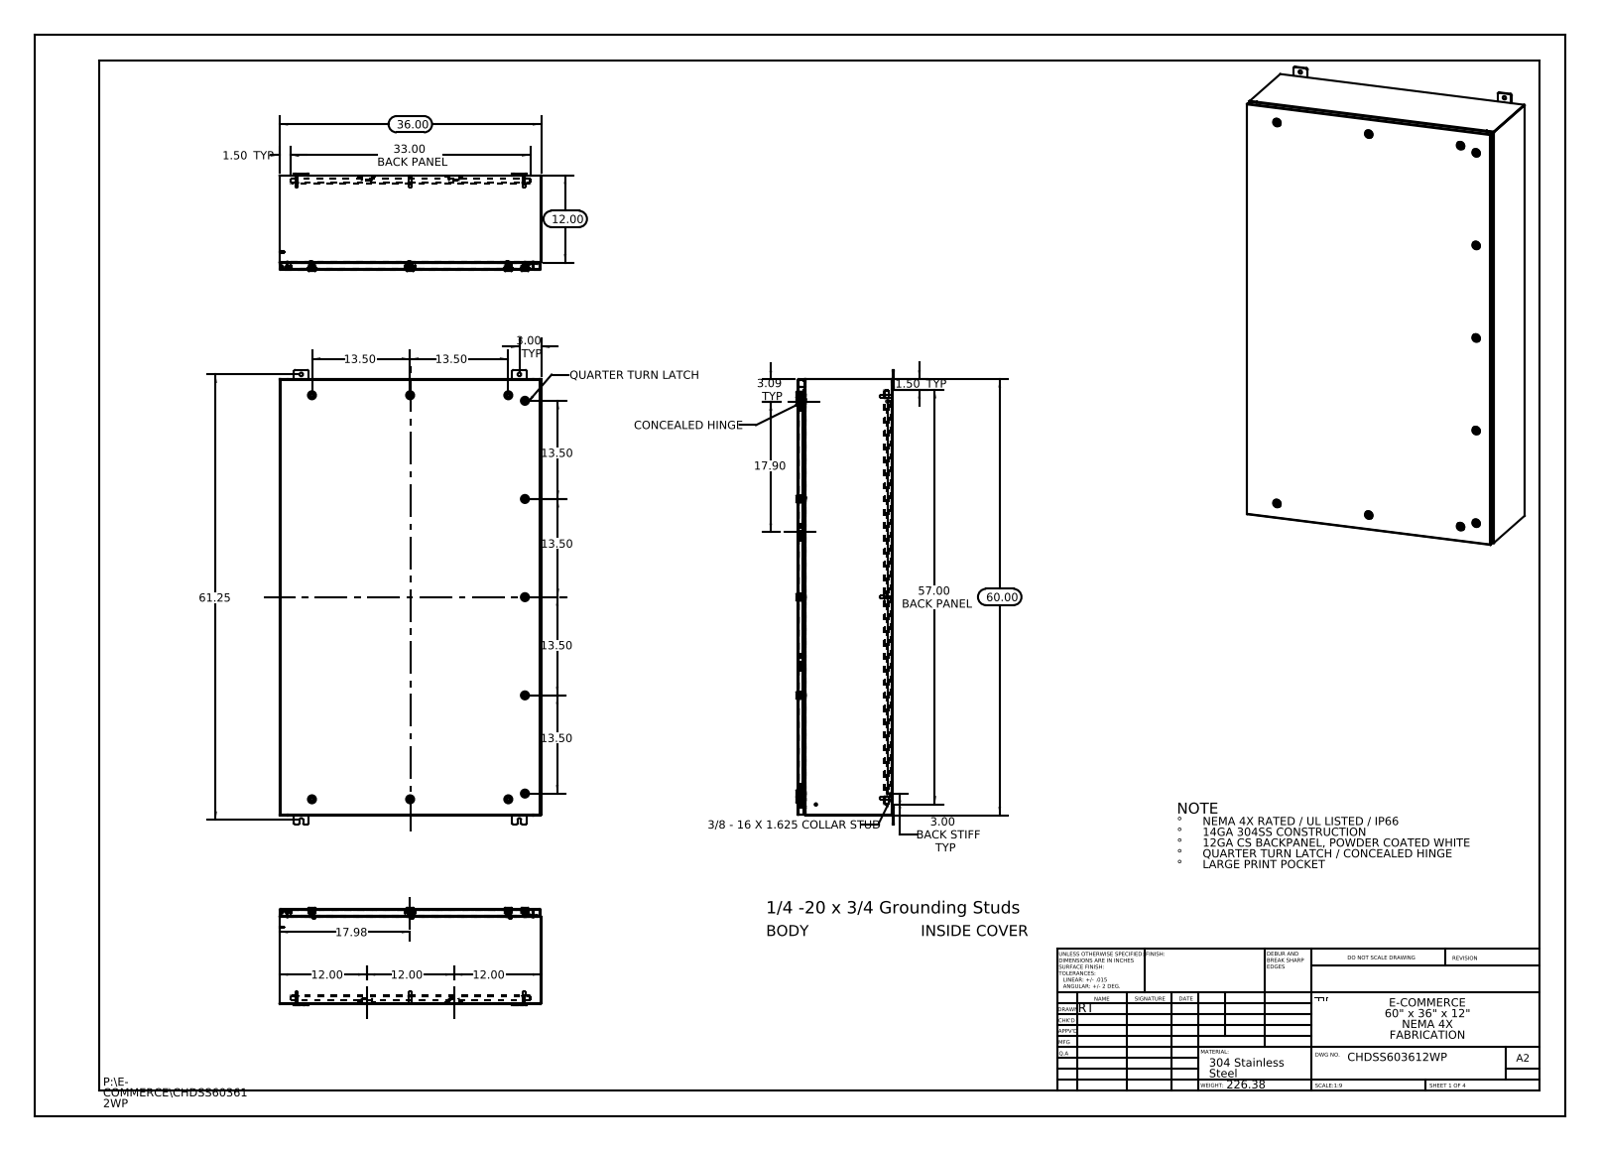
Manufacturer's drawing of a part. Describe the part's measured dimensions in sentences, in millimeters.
The part is named "Nut-211301-IB-Industrilas_Nut-211301-IB-Industrilas; CHDSS603612WP Enclosure Stiffener; CHDSS603612WP Top; Housing-211301-IB-Industrilas_Housing-211301-IB-Industrilas (+8 more)". Its 3-D file was written by "SolidWorks 2013 (CONFIG_CONTROL_DESIGN)". It is 104 solids with 9960 faces: 2880 planar, 3110 cylindrical and 3970 other. Overall it measures 1587.5 by 914.4 by 339.2 millimeters. Its volume is 13 080 000 cubic millimeters and its surface area 12 780 000 square millimeters. Round holes: 12 of diameter 12.7, 11 of diameter 5, 11 of diameter 10, 11 of diameter 10.2, 11 of diameter 16, 11 of diameter 20, 8 of diameter 3.5, 8 of diameter 6.4, 1 of diameter 5.4. Round bosses or shafts: 13 of diameter 6, 11 of diameter 28, 11 of diameter 19.8, 11 of diameter 15.9, 11 of diameter 15.5, 11 of diameter 13.5, 11 of diameter 10, 11 of diameter 2.9. Partial cylindrical surfaces (rounded edges, fillets, slot ends): 363 of radius 3, 360 of radius 0.2, 126 of radius 0.7, 36 of radius 5, 34 of radius 0.3, 32 of radius 0.5, 30 of radius 2.2, 24 of radius 4.8. The main face-to-face distances are 1.9, 1.9, 326.7, 328.6, 330.5, 328.5, 2.6, 25.4, 301.3, 27.3. The hole center spacings are 342.9, 454.6, 17.5, 56.5, 685.8, 701.7, 909.1, 1059.4.
